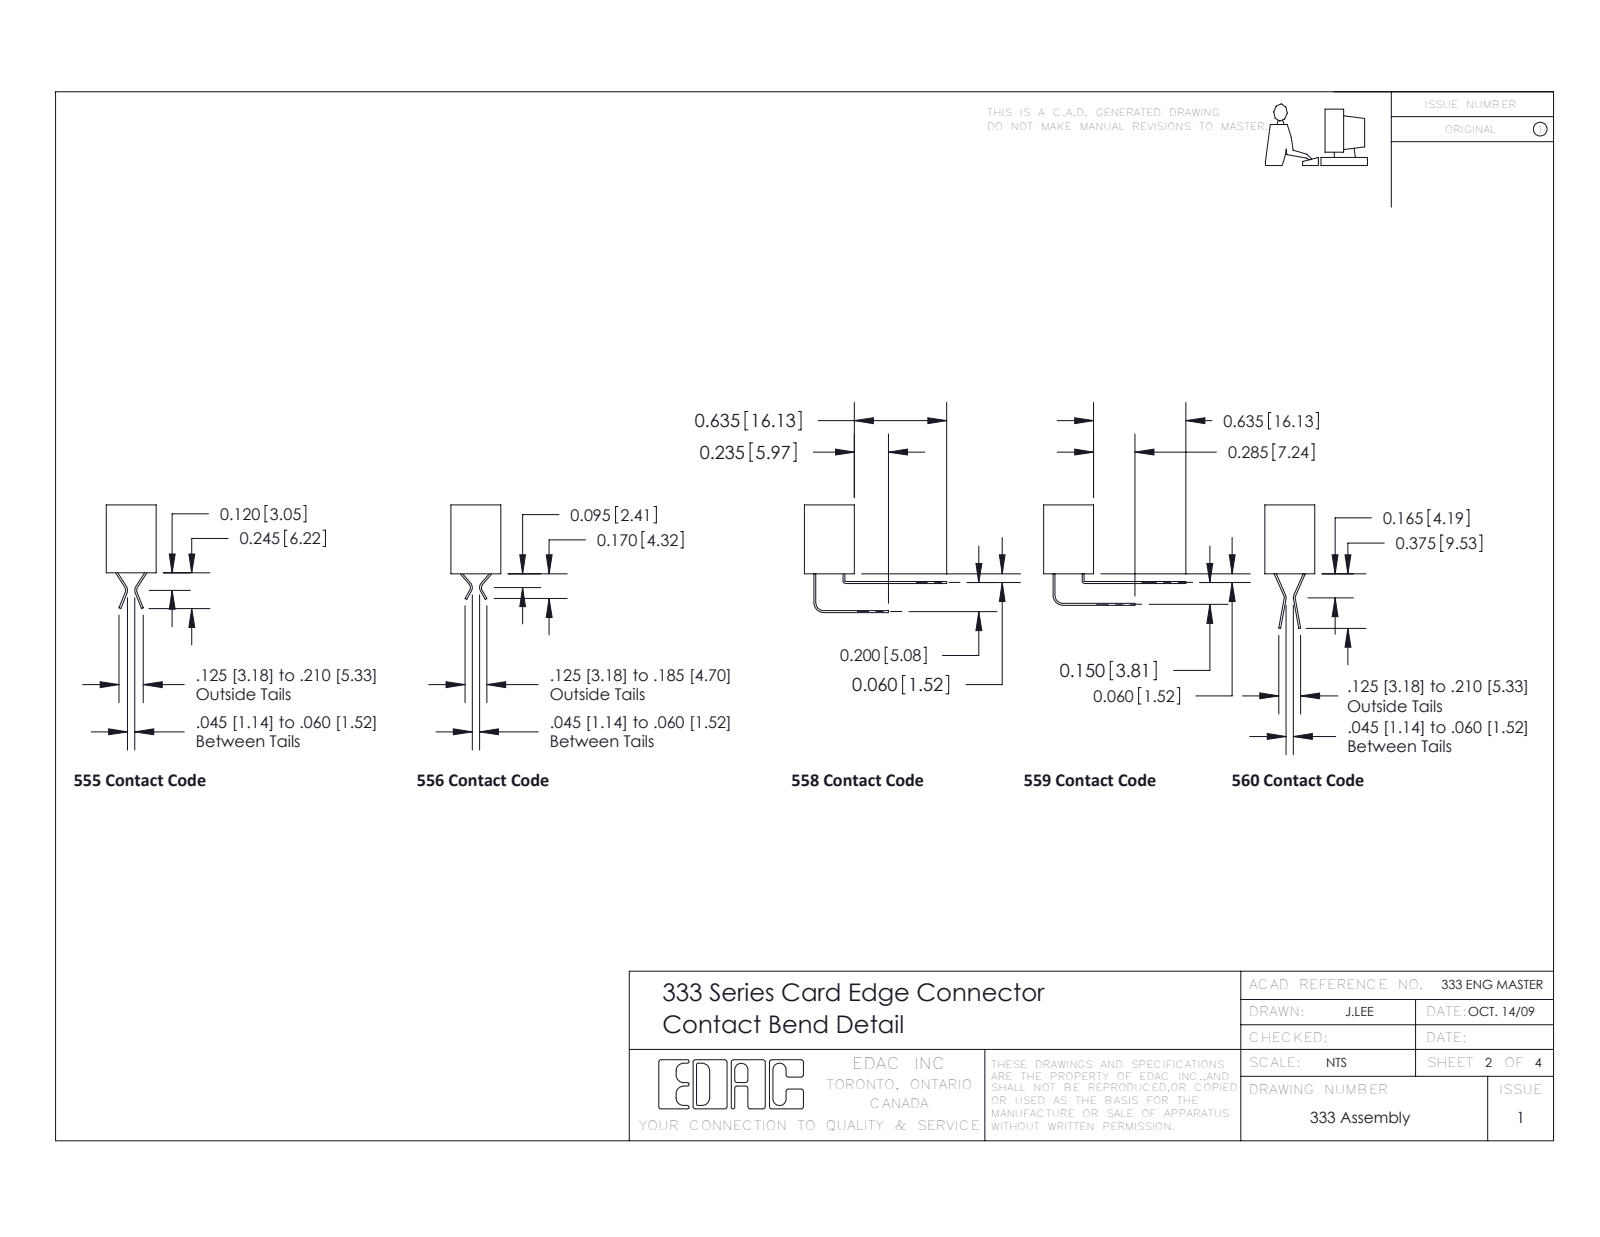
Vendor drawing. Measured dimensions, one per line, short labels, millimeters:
name: 333 Part_Flush - Side; 333-027-520-112; 345-292-001_345-293-120
written by: SolidWorks 2016 (CONFIG_CONTROL_DESIGN)
unit: mm
bodies: 28 solids, 1788 faces (1258 planar, 530 cylindrical, 0 other)
size: 128.5 × 20 × 9.4
volume: 12 600 mm³; area: 13 150 mm²
holes: 2× ⌀3.3
rounds: 56× R0.3, 54× R0.2, 22× R0.3, 6× R0.2, 6× R0.8, 3× R0.7, 1× R0.4, 1× R0.6
face distances: 9.4, 3.8, 5.6, 7.6, 1.8, 3.8, 1.9, 1.9, 14, 4
hole spacings: 122.2
